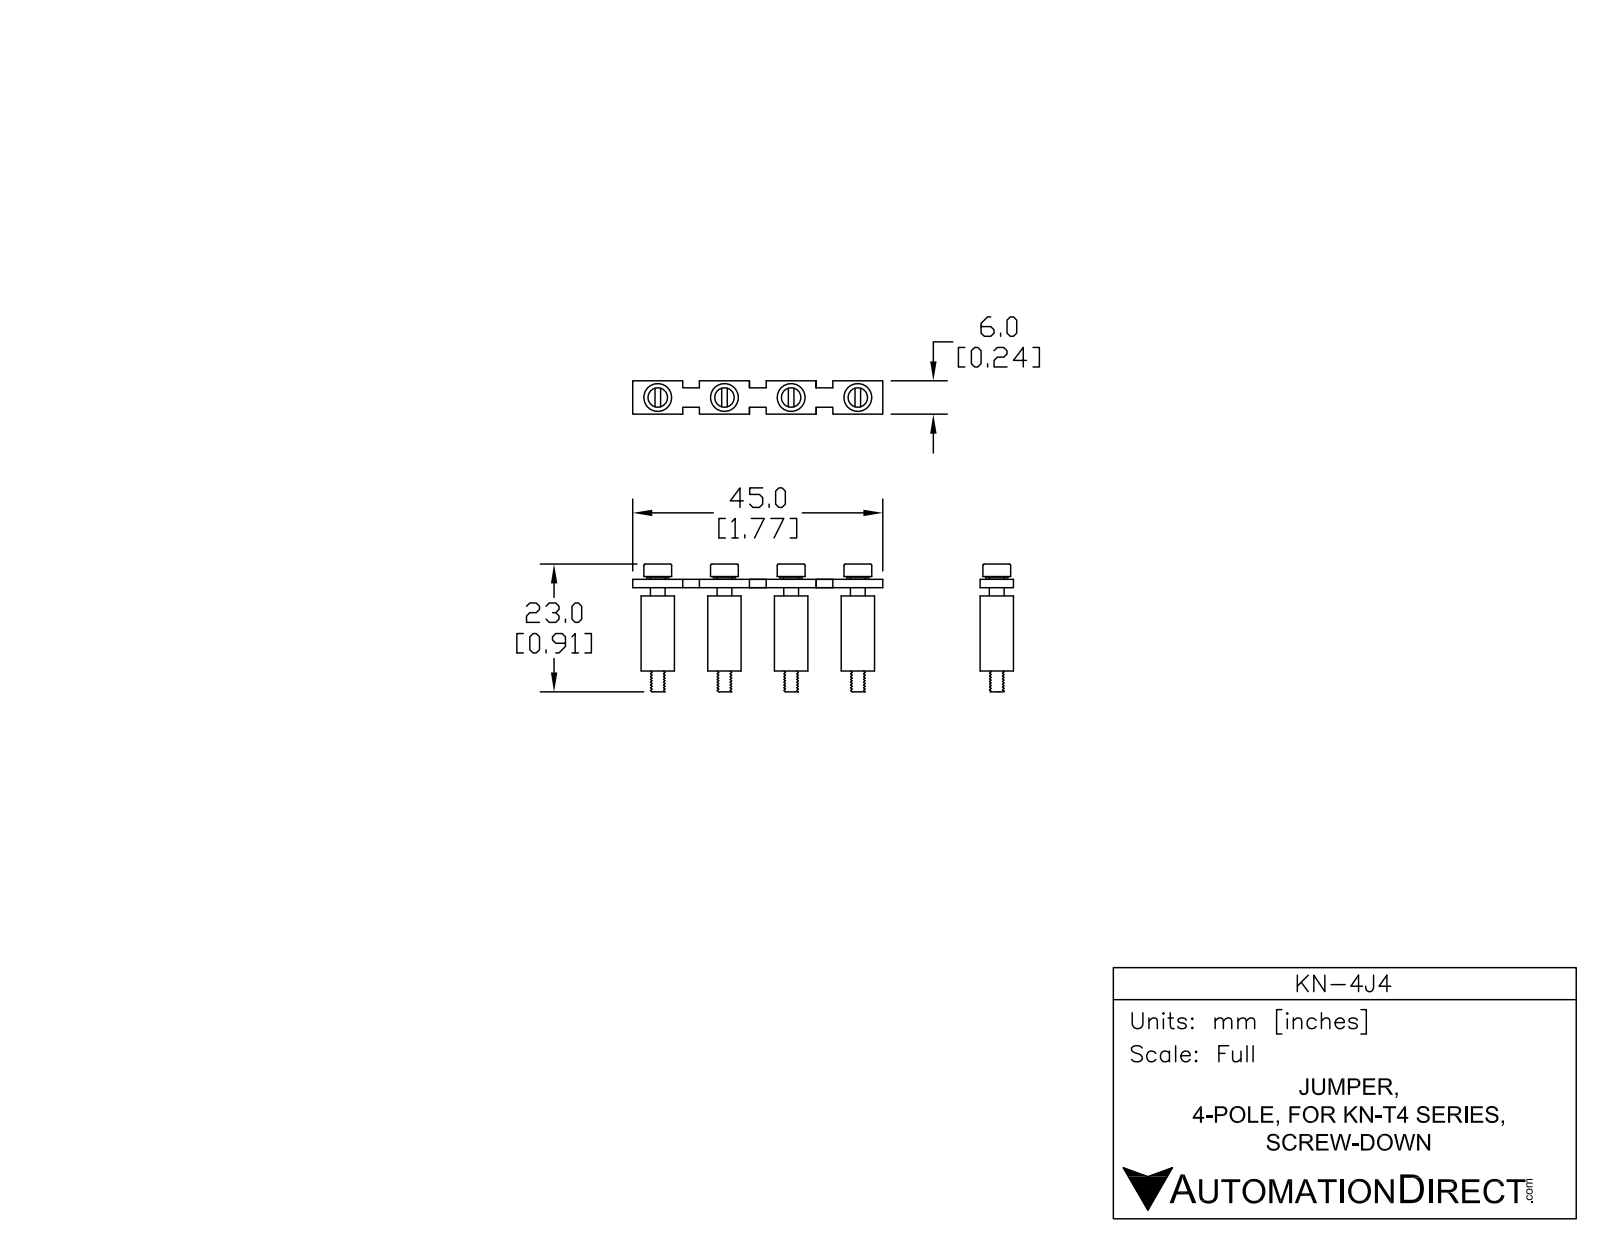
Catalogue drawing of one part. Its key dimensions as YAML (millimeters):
part_name: "KN-4J4"
step_written_by: "SolidWorks 2014 (AUTOMOTIVE_DESIGN)"
units: millimeters
bodies: {solids: 13, faces: 166, planar: 82, cylindrical: 60, other: 24}
overall_size: [45, 23, 6]
volume: 1901
surface_area: 3747
round_holes:
  - {diameter: 3.15, count: 4}
  - {diameter: 3.5, count: 4}
round_bosses_or_shafts:
  - {diameter: 6, count: 4}
  - {diameter: 5, count: 4}
  - {diameter: 4, count: 4}
  - {diameter: 2.65, count: 4}
face_to_face_distances: [1.5, 3, 15, 16.5, 13.5, 2, 0.5, 17, 1.75, 2.25]
hole_center_spacings: [12, 24, 36]
